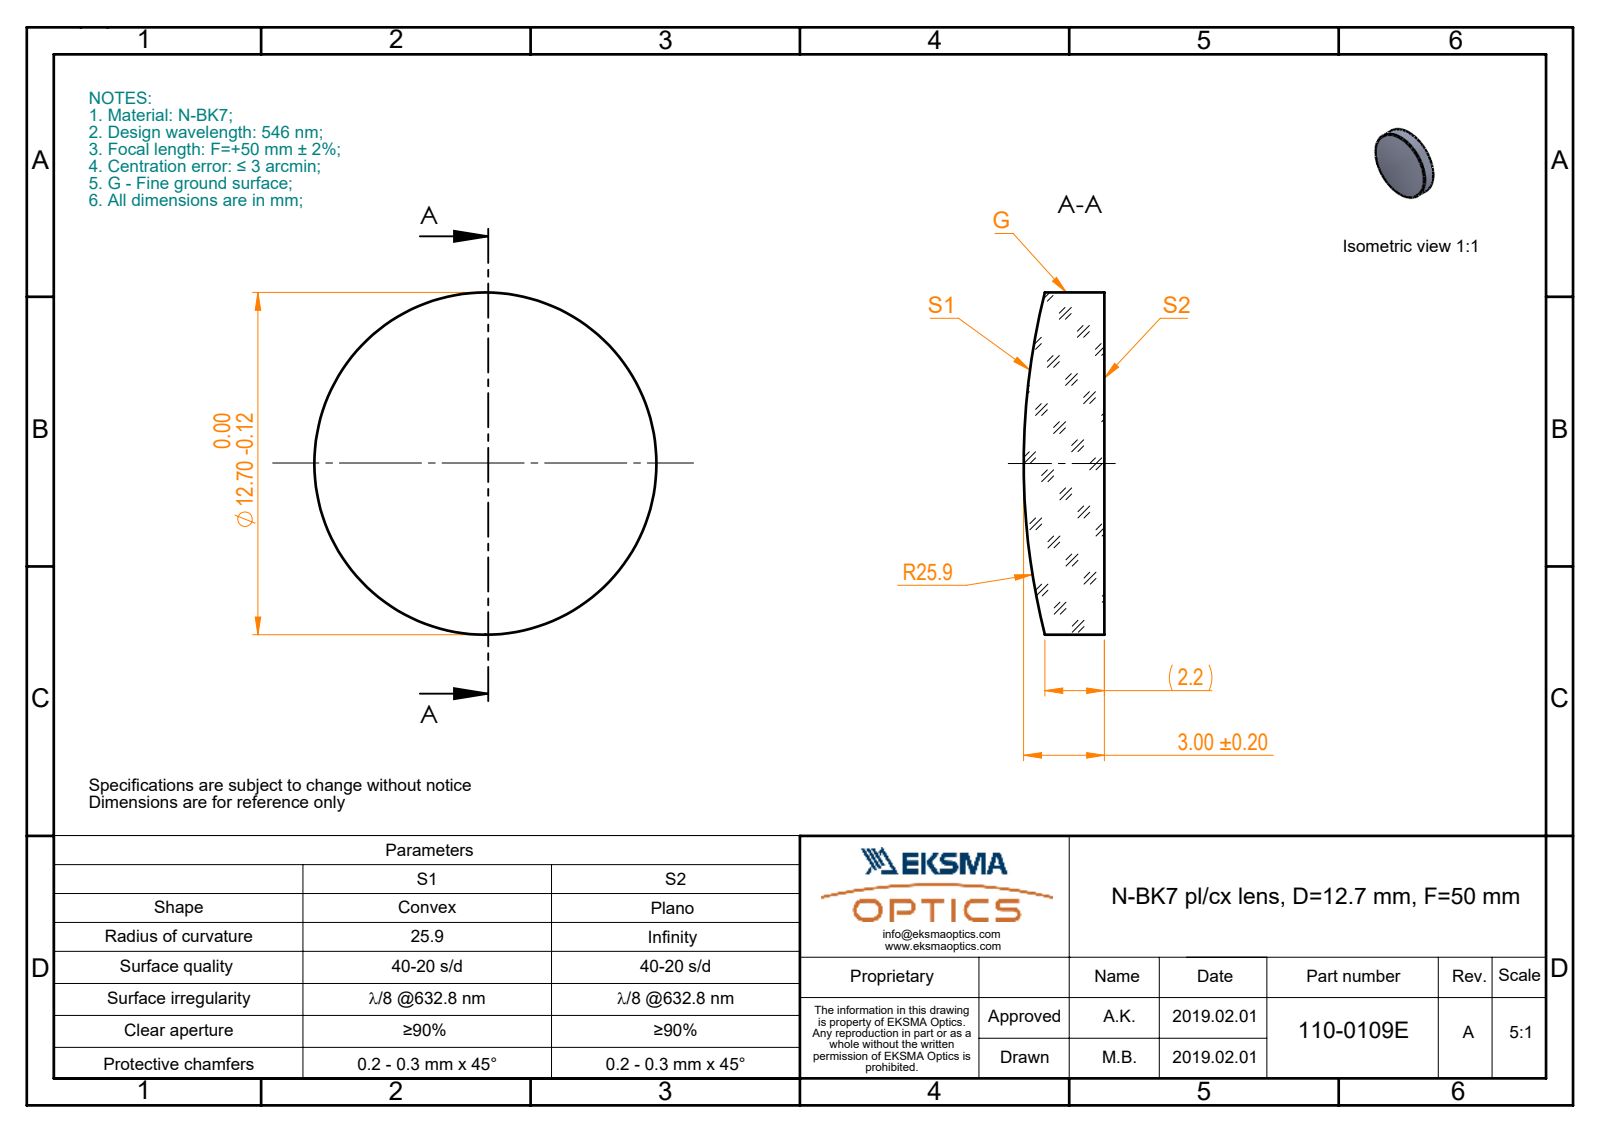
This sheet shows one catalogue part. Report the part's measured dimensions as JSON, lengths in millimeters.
{"part_name": "110-0109E BK7 pl-cx 12.7 F50", "step_written_by": "SolidWorks 2017 (CONFIG_CONTROL_DESIGN)", "units": "millimeters", "bodies": {"solids": 1, "faces": 5, "planar": 1, "cylindrical": 2, "other": 2}, "overall_size": [12.7, 12.7, 3], "volume_mm3": 330, "surface_area_mm2": 344, "round_bosses_or_shafts": [[12.7, 1]]}
